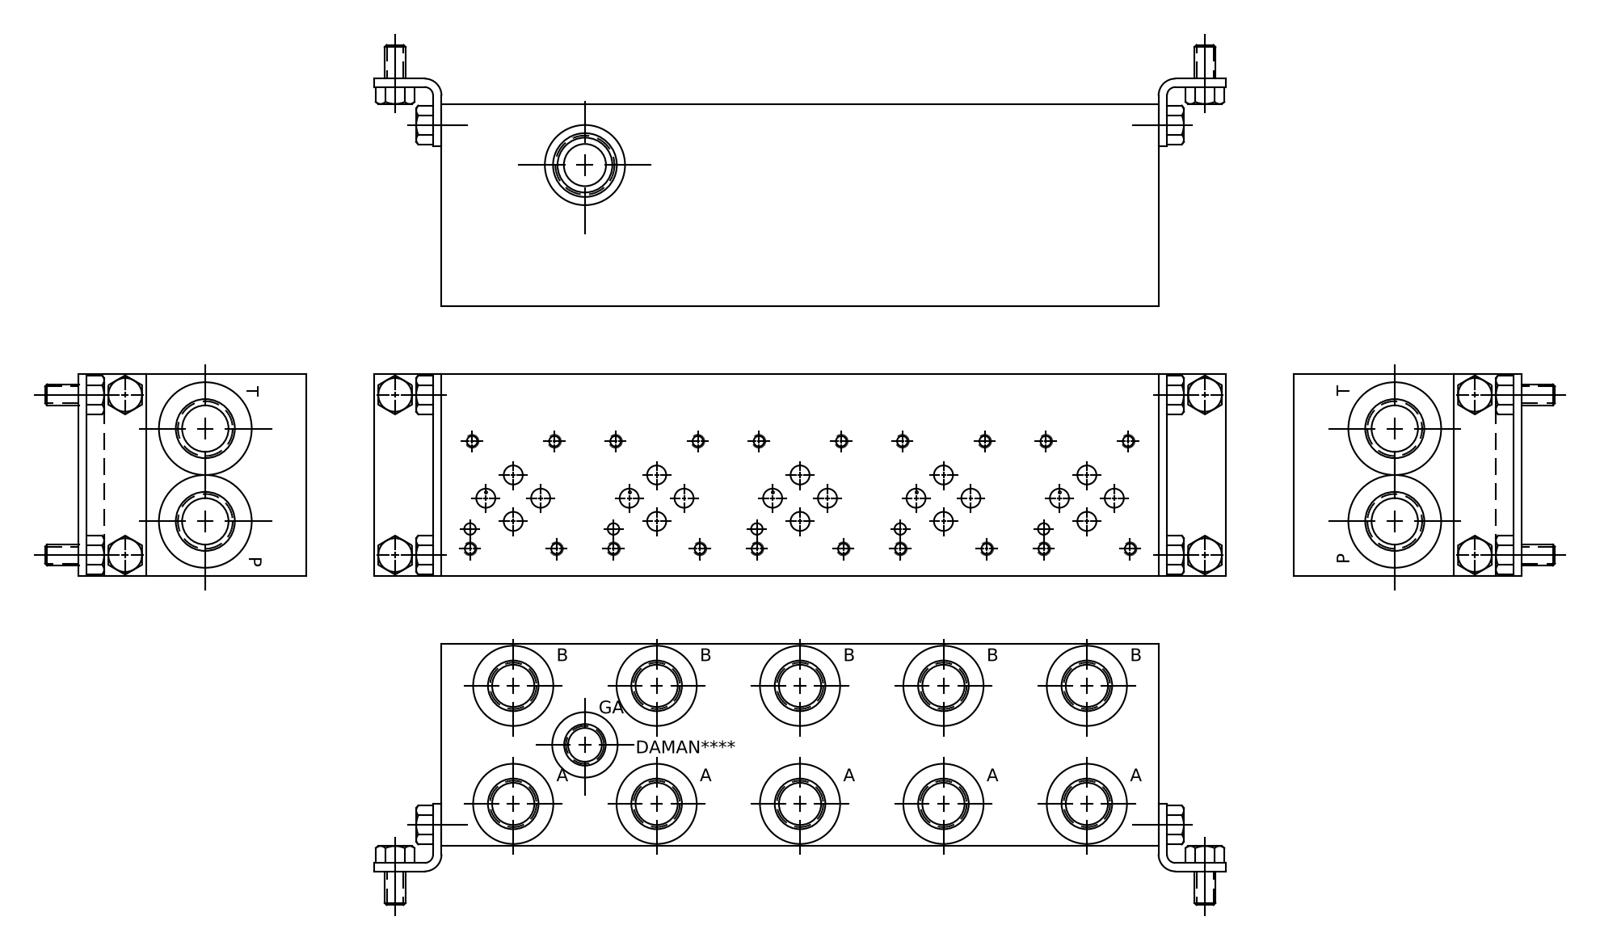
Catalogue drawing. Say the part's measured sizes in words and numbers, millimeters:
The part is named "Part_AD03P052S_C_3D". Its 3-D file was written by "Autodesk Inventor 2020 (AUTOMOTIVE_DESIGN)". It is 1 solid with 957 faces: 466 planar, 154 cylindrical and 337 other. Overall it measures 270 by 76.2 by 76.2 millimeters. Its volume is 1 429 000 cubic millimeters and its surface area 126 589 square millimeters. Round holes: 20 of diameter 3.78, 20 of diameter 4.83, 15 of diameter 7.14, 10 of diameter 15.88, 10 of diameter 17.5, 10 of diameter 19.05, 10 of diameter 19.25, 10 of diameter 30.63, 5 of diameter 3.96, 5 of diameter 6.35, 3 of diameter 22.23, 2 of diameter 6.53. The main face-to-face distances are 76.2, 0.79, 75.41, 270, 269.21, 268.42, 15.06, 14.27, 61.14, 0.75. The hole center spacings are 54.1, 13.52, 107.95, 54.11, 108.21, 216.16, 12.99, 13.53.
